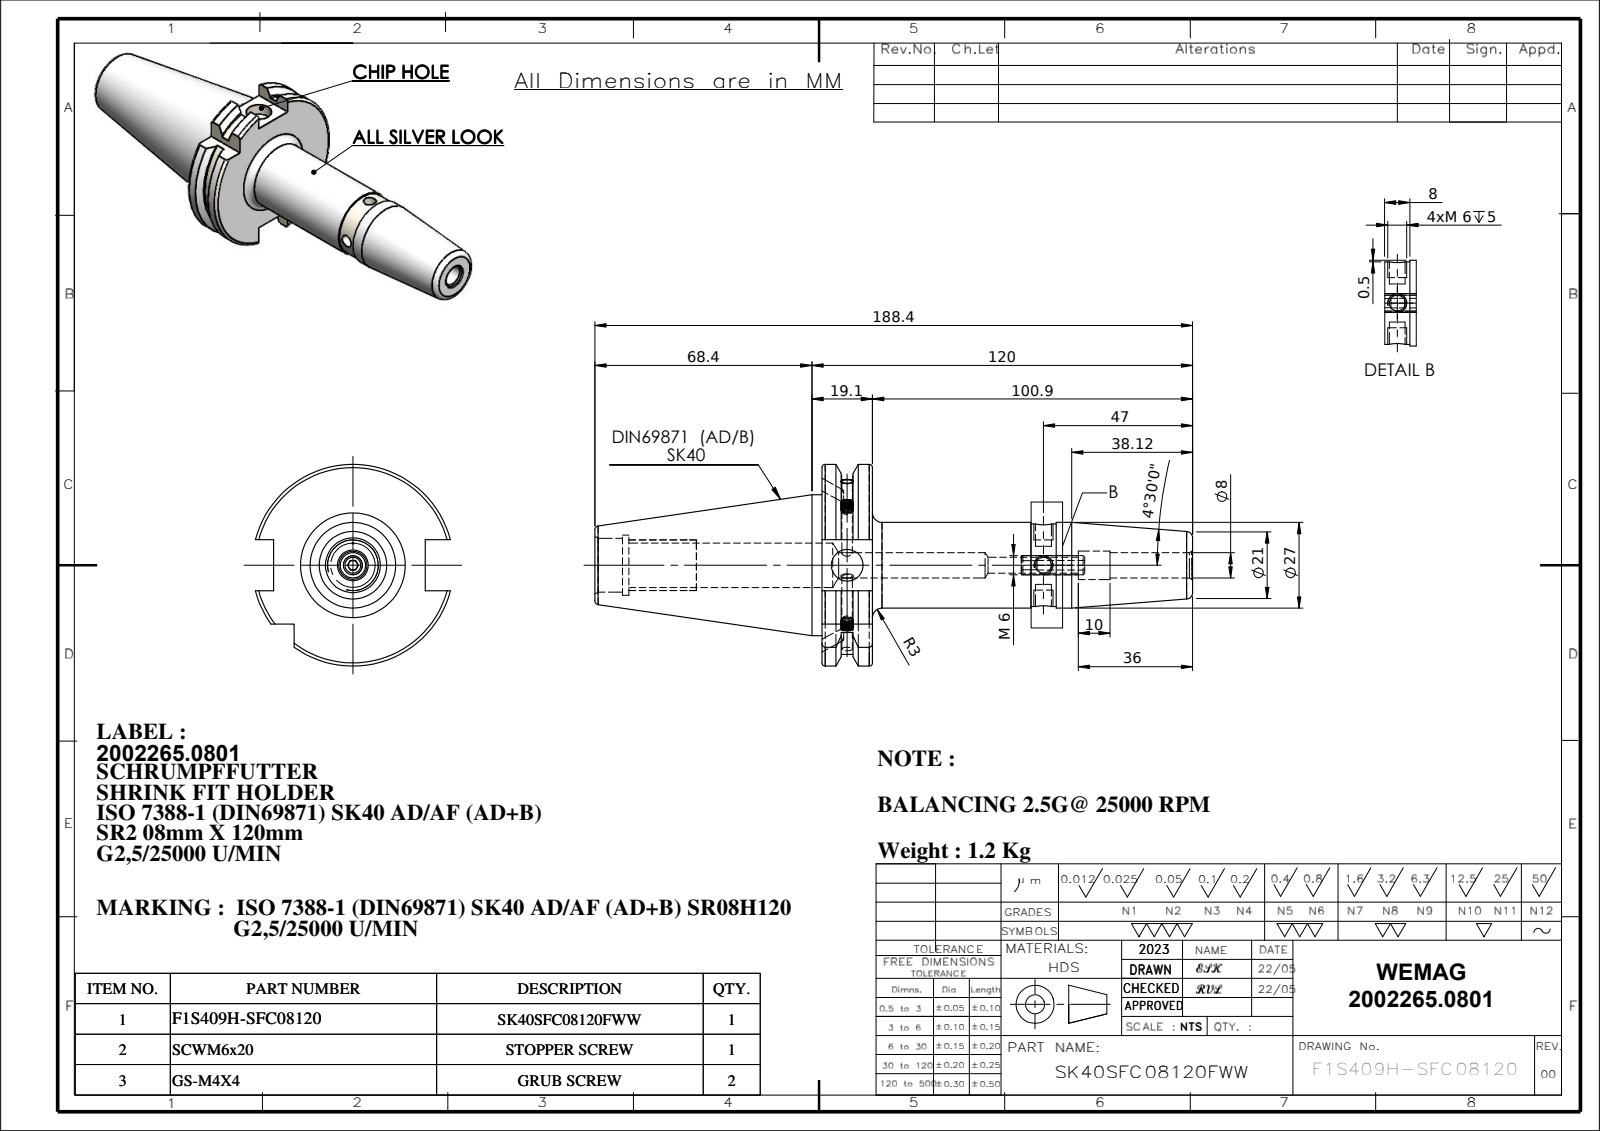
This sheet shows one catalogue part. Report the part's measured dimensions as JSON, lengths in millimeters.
{"part_name": "SCWM6; SK40SFC08120FWW; 91406-SR208120; GS-M4X4_DIN 913 - M4 x 4-N", "step_written_by": "SolidWorks 2018 (CONFIG_CONTROL_DESIGN)", "units": "millimeters", "bodies": {"solids": 4, "faces": 237, "planar": 63, "cylindrical": 72, "other": 102}, "overall_size": [188.4, 63.55, 61.48], "volume_mm3": 148150, "surface_area_mm2": 32746, "round_holes": [[5, 3], [2.9, 1], [3.3, 1], [7.99, 1], [8, 1], [8.99, 1], [10, 1], [14, 1], [17, 1], [19, 1]], "round_bosses_or_shafts": [[4, 2], [44.45, 1], [27, 1], [26, 1], [6, 1]], "partial_cylinders_radius": [[28.12, 1], [31.77, 1]], "face_to_face_distances": [15.9, 16.1, 47.8, 116.8, 100.9, 71.6, 87.5, 188.4, 10.7, 60.9], "hole_center_spacings": [61.85]}
